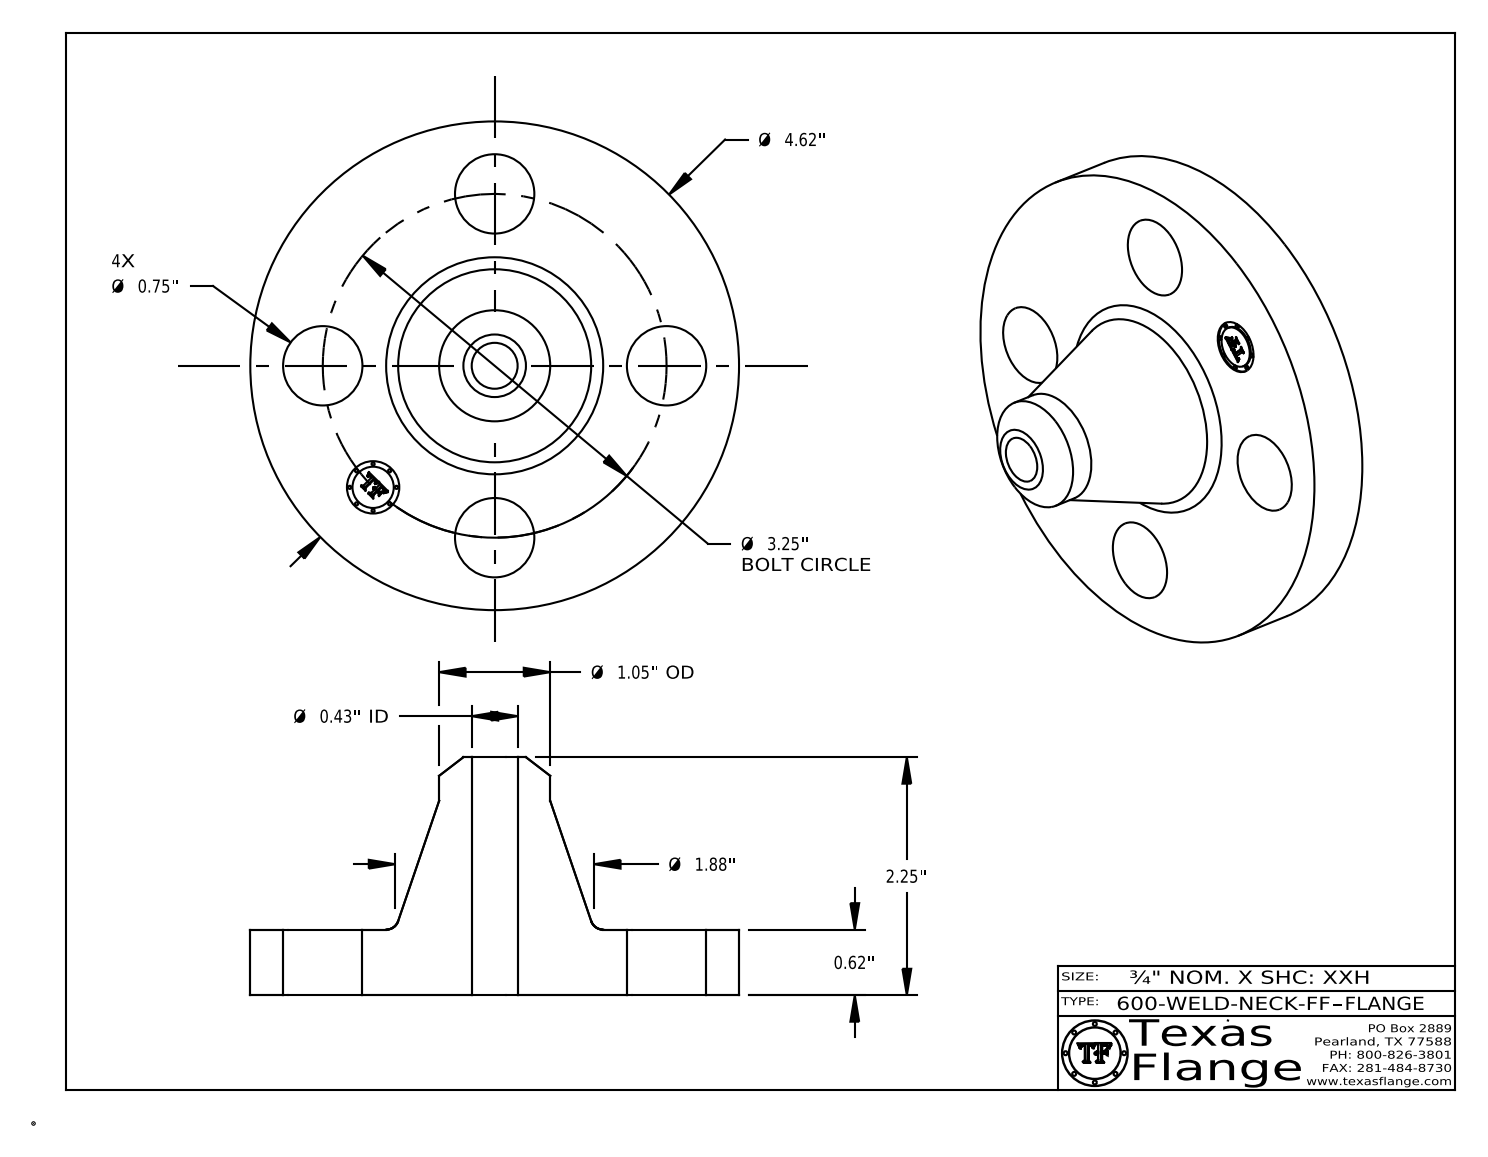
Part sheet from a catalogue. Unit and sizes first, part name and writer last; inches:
Units: inches
Overall size (bounding box): 4.62 × 4.62 × 2.25
Round holes (diameter × count): ⌀0.75 ×4, ⌀0.434 ×1, ⌀0.495 ×1
Round bosses / shafts (diameter × count): ⌀0.03 ×8, ⌀4.62 ×1, ⌀1.05 ×1, ⌀0.39 ×1
Main face-to-face distances: 0.62, 2.25, 1.63, 0.605, 0.015, 1.645, 0.148, 0.144, 0.027, 0.096
Hole centre spacings: 1.625, 2.298, 1.244, 3.003, 3.25
Volume: 11.38 in³ · Surface area: 52.52 in²
Bodies: 1 solid, 408 faces (368 planar, 34 cylindrical, 6 other)
Part name (STEP PRODUCT): 600-WELD-NECK-FF
STEP written by: CATIA V5 STEP AP214 (AUTOMOTIVE_DESIGN)
